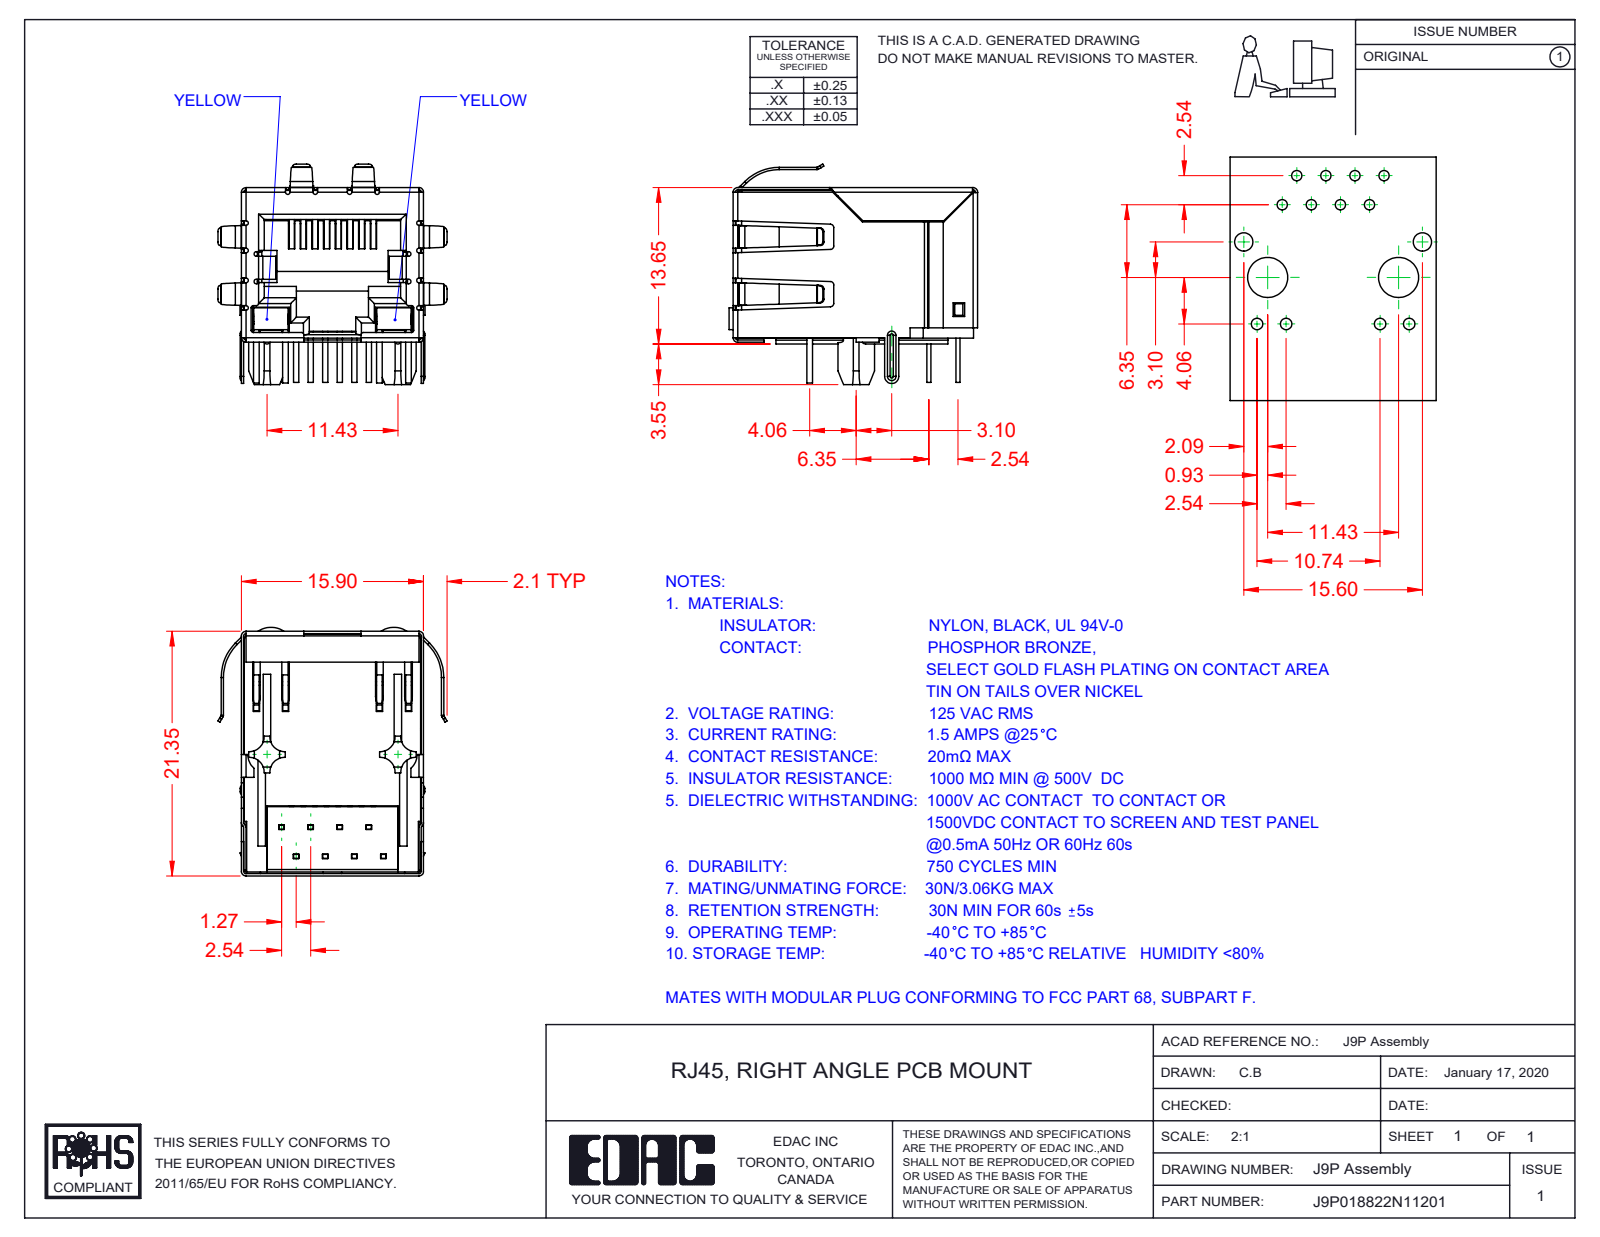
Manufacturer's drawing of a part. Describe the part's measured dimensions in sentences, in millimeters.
The part is named "9P-LED Insulator; 9P-LED Assembly; 9P-LED Contacts; 9P-LED LED RH_1-Yellow (+4 more)". Its 3-D file was written by "SolidWorks 2016 (CONFIG_CONTROL_DESIGN)". It is 13 solids with 1472 faces: 1042 planar, 336 cylindrical and 94 other. Overall it measures 21.7 by 20 by 19.25 millimeters. Its volume is 2 687 cubic millimeters and its surface area 7 515 square millimeters. Partial cylindrical surfaces (rounded edges, fillets, slot ends): 39 of radius 0.2, 22 of radius 0.5, 20 of radius 0.3, 16 of radius 0.4, 8 of radius 1.3, 5 of radius 0.23, 4 of radius 0.11, 4 of radius 0.31. The main face-to-face distances are 15.45, 15.7, 15.65, 0.35, 0.54, 15.5, 12.36, 0.6, 1.4, 0.59.
